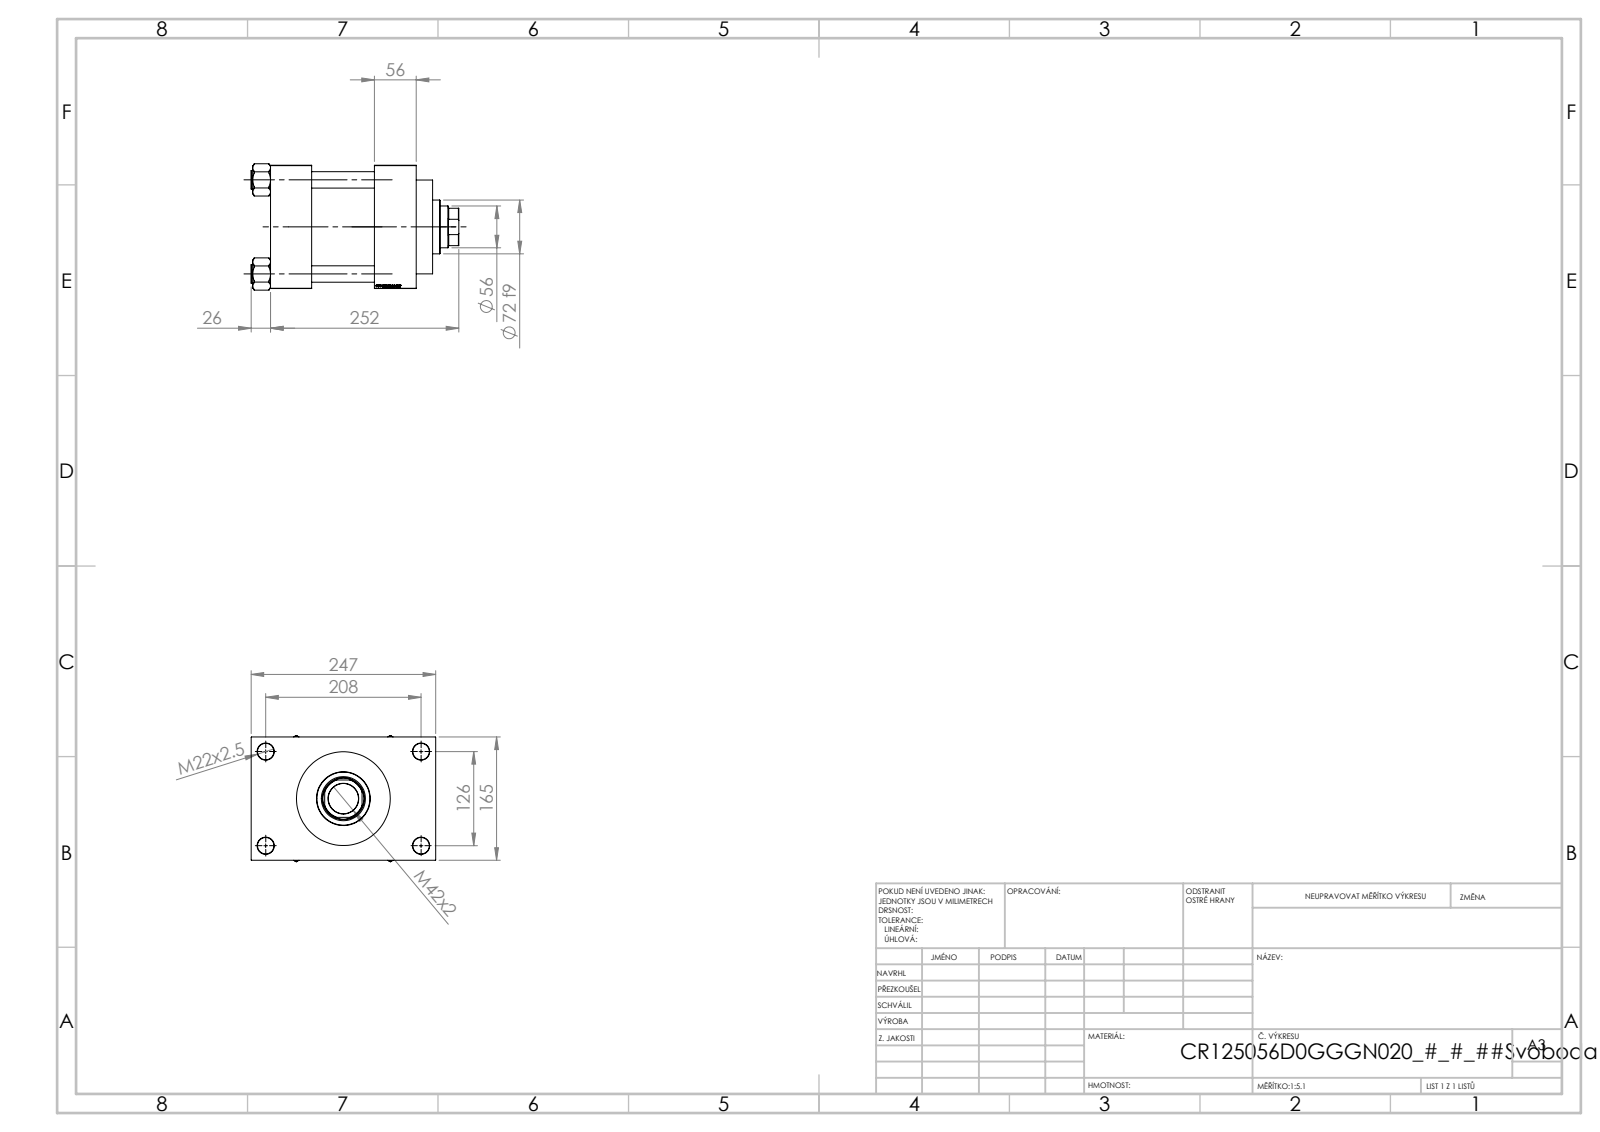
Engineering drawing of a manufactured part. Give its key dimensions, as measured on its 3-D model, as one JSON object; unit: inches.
{"part_name": "V215CR_D_Body; V215_VC_A; NUT_M5_D; V215CR_VCP_D (+1 more)", "step_written_by": "SolidWorks 2019 (CONFIG_CONTROL_DESIGN)", "units": "inches", "bodies": {"solids": 11, "faces": 1149, "planar": 544, "cylindrical": 87, "other": 518}, "overall_size": [10.945, 9.724, 6.659], "volume_in3": 302.6, "surface_area_in2": 821.4, "round_holes": [[0.866, 8], [0.276, 2], [1.269, 2], [1.772, 2], [1.594, 1], [2.205, 1], [2.323, 1], [3.78, 1], [4.921, 1], [4.941, 1]], "round_bosses_or_shafts": [[0.984, 4], [5.157, 1], [2.835, 1]], "partial_cylinders_radius": [[1.063, 1]], "face_to_face_distances": [6.496, 3.307, 2.165, 5.472, 2.205, 7.677, 5.512, 1.614, 8.11, 6.84], "hole_center_spacings": [1.616, 3.505, 4.787, 4.957, 5.215, 6.573, 8.233, 4.961]}
